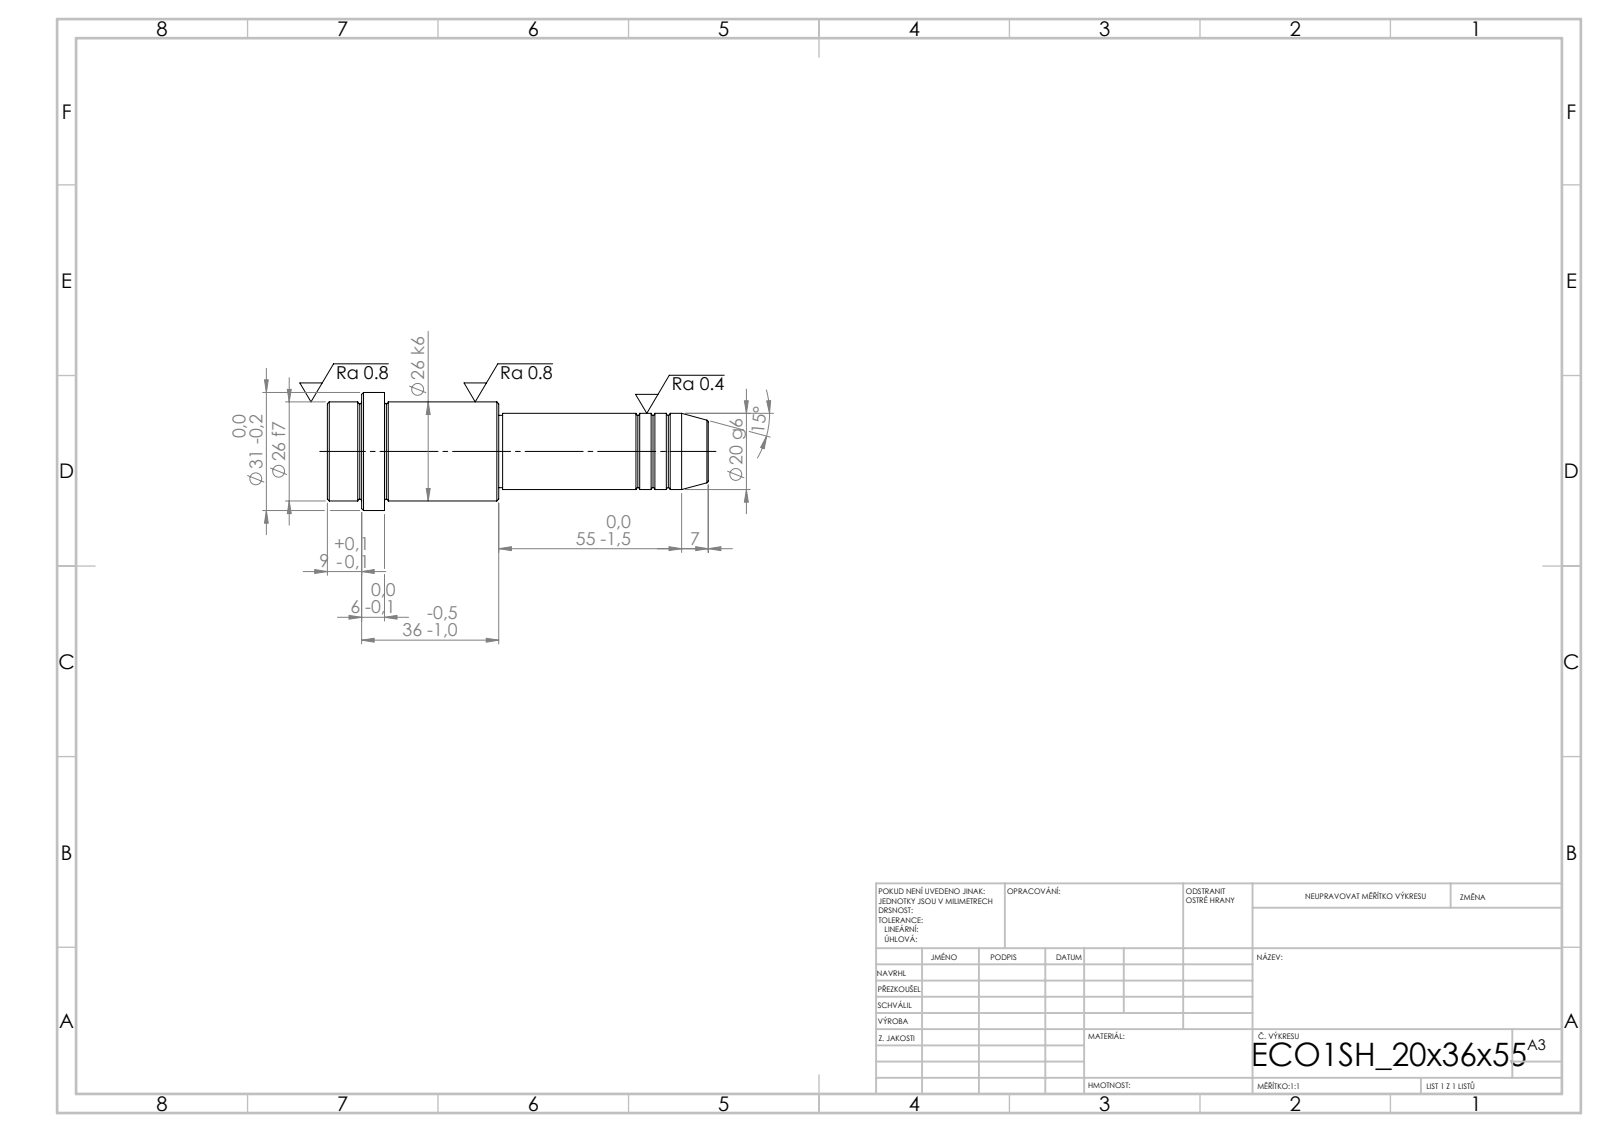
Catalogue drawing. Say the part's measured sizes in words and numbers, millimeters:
Its 3-D file was written by "SolidWorks 2019 (CONFIG_CONTROL_DESIGN)". It is 1 solid with 52 faces: 6 planar, 16 cylindrical and 30 other. Overall it measures 100 by 31 by 31 millimeters. Its volume is 41 927 cubic millimeters and its surface area 8 761 square millimeters. Round bosses or shafts: 1 of diameter 31, 1 of diameter 26, 1 of diameter 20, 1 of diameter 19. The main face-to-face distances are 15, 30, 45, 55, 85, 100, 91, 36, 6, 9.
